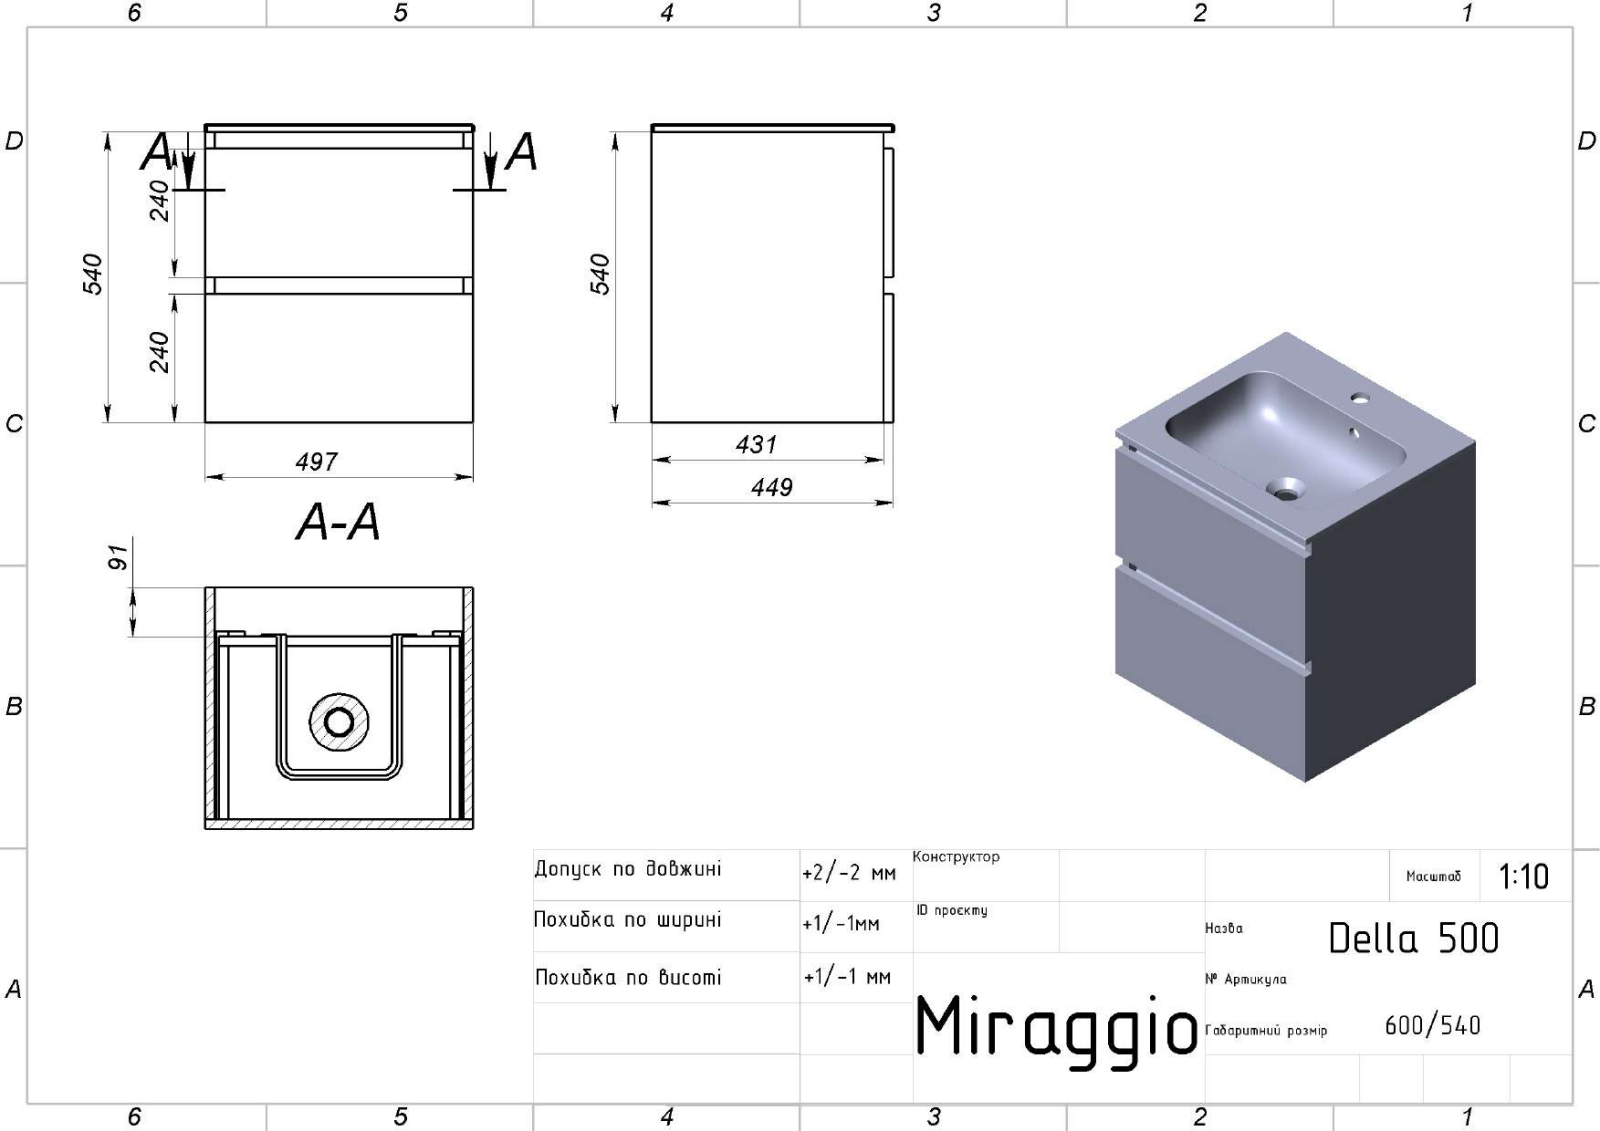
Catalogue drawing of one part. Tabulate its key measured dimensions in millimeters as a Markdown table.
| quantity | value |
| --- | --- |
| STEP written by | Rhino 7.13 (CONFIG_CONTROL_DESIGN) |
| units | millimeters |
| bodies | 24 solids, 2302 faces (1618 planar, 337 cylindrical, 347 other) |
| overall size | 554 × 500.98 × 455.15 |
| volume | 30 860 000 mm³ |
| surface area | 4 497 000 mm² |
| round holes (diameter × count) | 4 × 16, 6.2 × 6, 5.51 × 2, 25 × 1, 35 × 1, 45 × 1 |
| round bosses / shafts (diameter × count) | 8 × 6, 20 × 2, 9 × 2, 5.5 × 2 |
| partial cylindrical surfaces (radius × count) | 1.5 × 44, 2 × 30, 3.5 × 16, 4 × 14, 0.2 × 10, 0.1 × 8, 7 × 6, 1 × 5 |
| main face-to-face distances | 18, 479, 24.5, 454.5, 48.5, 461, 255.02, 42.5, 497, 436.5 |
| hole center spacings | 32, 64, 71.55, 45.25, 255.02, 26, 70, 90.51 |
